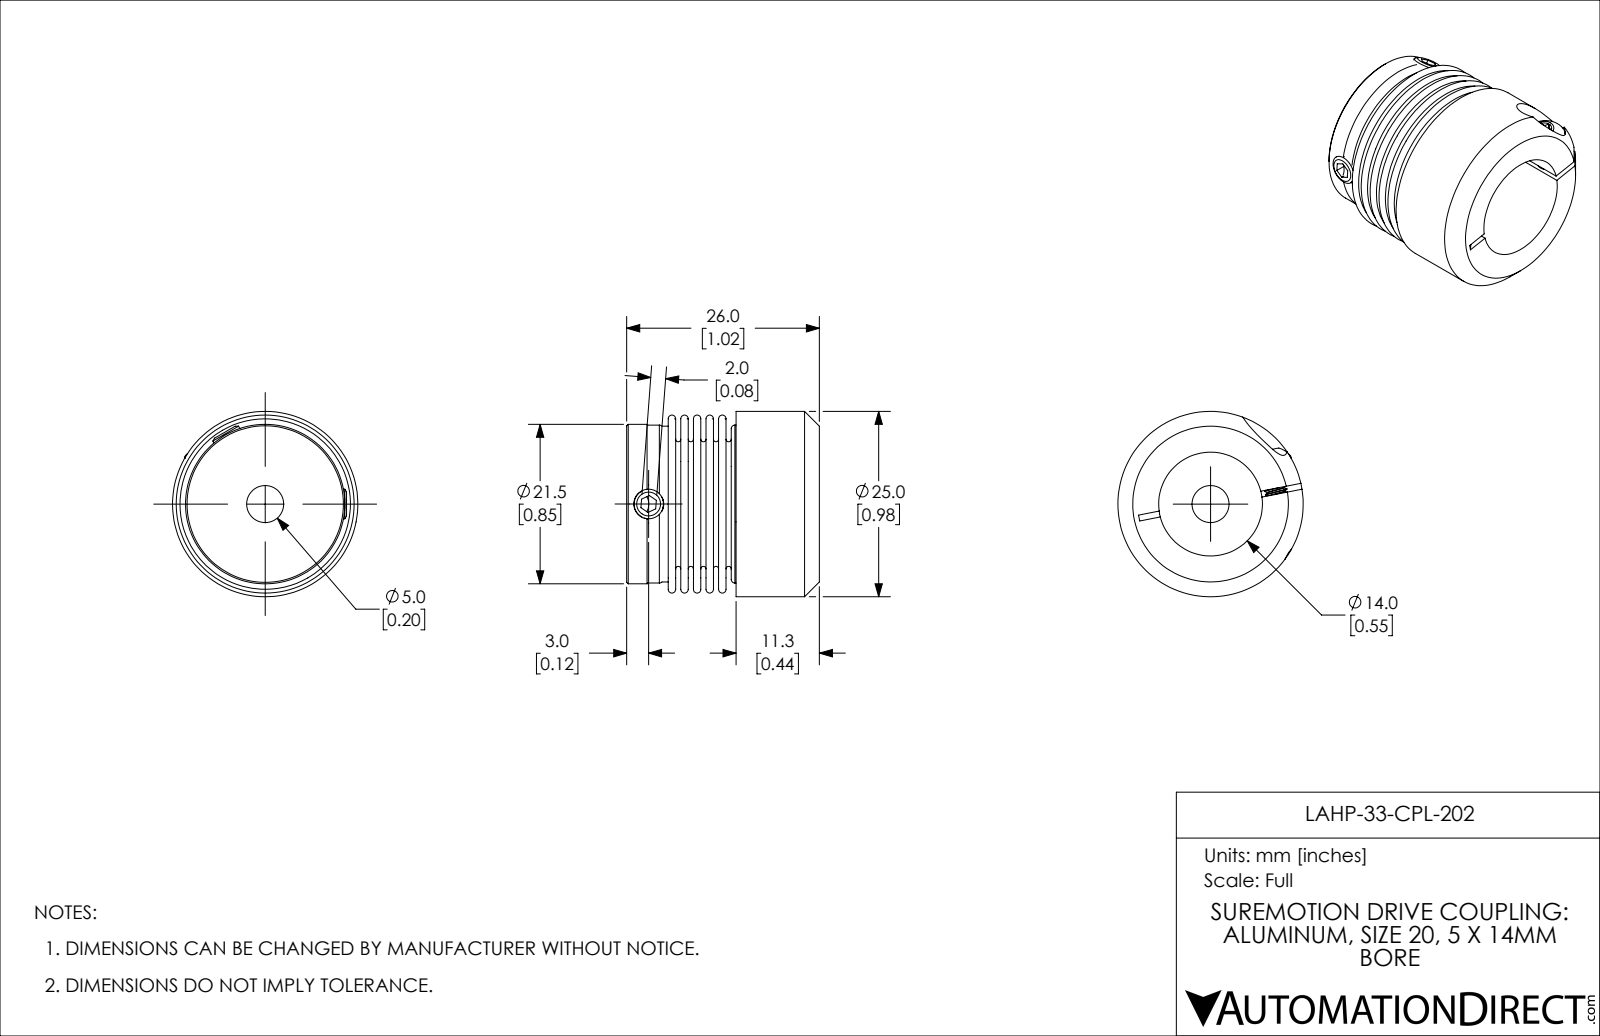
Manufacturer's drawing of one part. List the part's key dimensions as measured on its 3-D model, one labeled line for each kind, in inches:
Part name (STEP PRODUCT): LAHP-33-CPL-202
STEP written by: SolidWorks 2019 (CONFIG_CONTROL_DESIGN)
Units: inches
Bodies: 6 solids, 264 faces (58 planar, 100 cylindrical, 106 other)
Overall size (bounding box): 1.024 × 0.984 × 0.984
Volume: 0.372 in³ · Surface area: 16.58 in²
Round holes (diameter × count): ⌀0.157 ×2, ⌀0.126 ×1, ⌀0.197 ×1, ⌀0.228 ×1, ⌀0.551 ×1, ⌀0.827 ×1
Round bosses / shafts (diameter × count): ⌀0.157 ×2, ⌀0.984 ×1, ⌀0.846 ×1, ⌀0.839 ×1, ⌀0.224 ×1, ⌀0.118 ×1
Partial cylindrical surfaces — rounded edges, fillets, slot ends (radius × count): R0.024 ×6, R0.087 ×4, R0.047 ×1, R0.984 ×1
Main face-to-face distances: 0.067, 0.033, 0.1, 0.134, 0.167, 0.039, 0.073, 0.028, 0.106, 0.234
